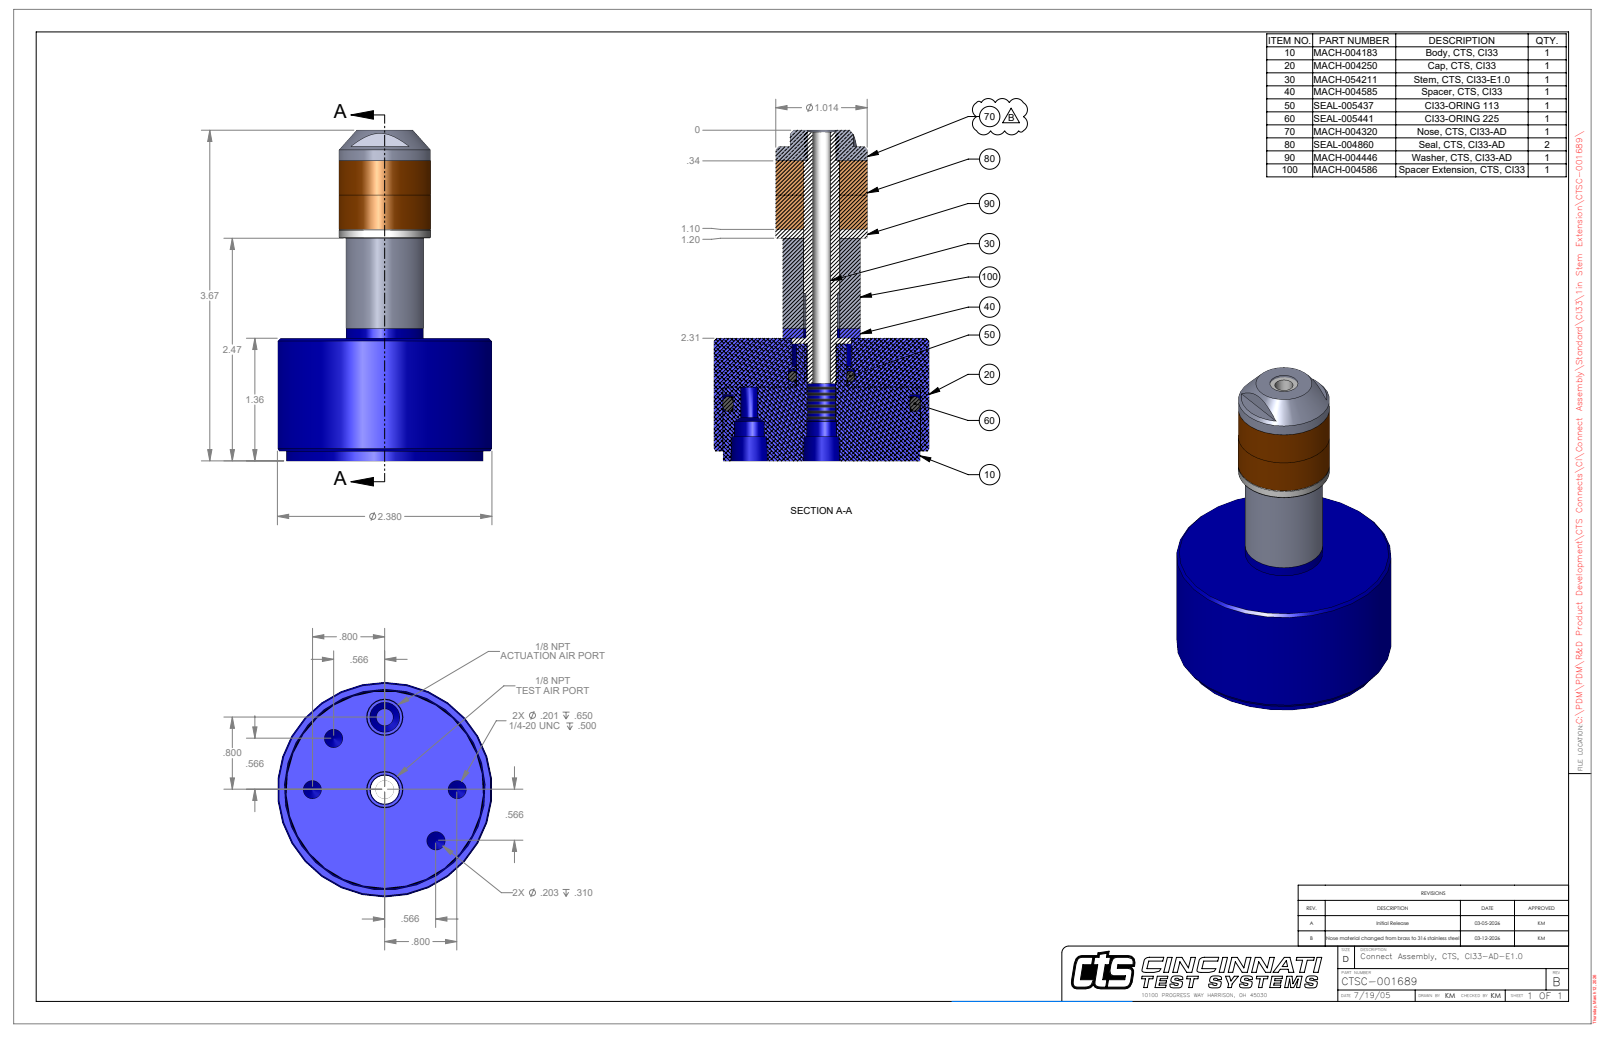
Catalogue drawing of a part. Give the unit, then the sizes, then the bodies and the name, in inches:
Units: inches
Overall size (bounding box): 3.667 × 2.38 × 2.38
Round holes (diameter × count): ⌀0.201 ×2, ⌀0.203 ×2, ⌀0.203 ×1, ⌀0.313 ×1, ⌀0.332 ×1, ⌀0.39 ×1, ⌀0.403 ×1, ⌀0.659 ×1, ⌀2.188 ×1
Round bosses / shafts (diameter × count): ⌀2.38 ×1, ⌀2.178 ×1, ⌀1.014 ×1, ⌀0.858 ×1, ⌀0.65 ×1, ⌀0.391 ×1, ⌀0.375 ×1
Main face-to-face distances: 1.36, 3.327, 1.967, 2.947, 1.587, 0.38, 1.207, 2.567, 0.38, 0.76
Hole centre spacings: 0.8, 0.612, 1.478, 1.6
Volume: 7.294 in³ · Surface area: 41.73 in²
Bodies: 7 solids, 74 faces (35 planar, 26 cylindrical, 13 other)
Part name (STEP PRODUCT): CTSC-001689
STEP written by: SolidWorks 2023 (AUTOMOTIVE_DESIGN)
